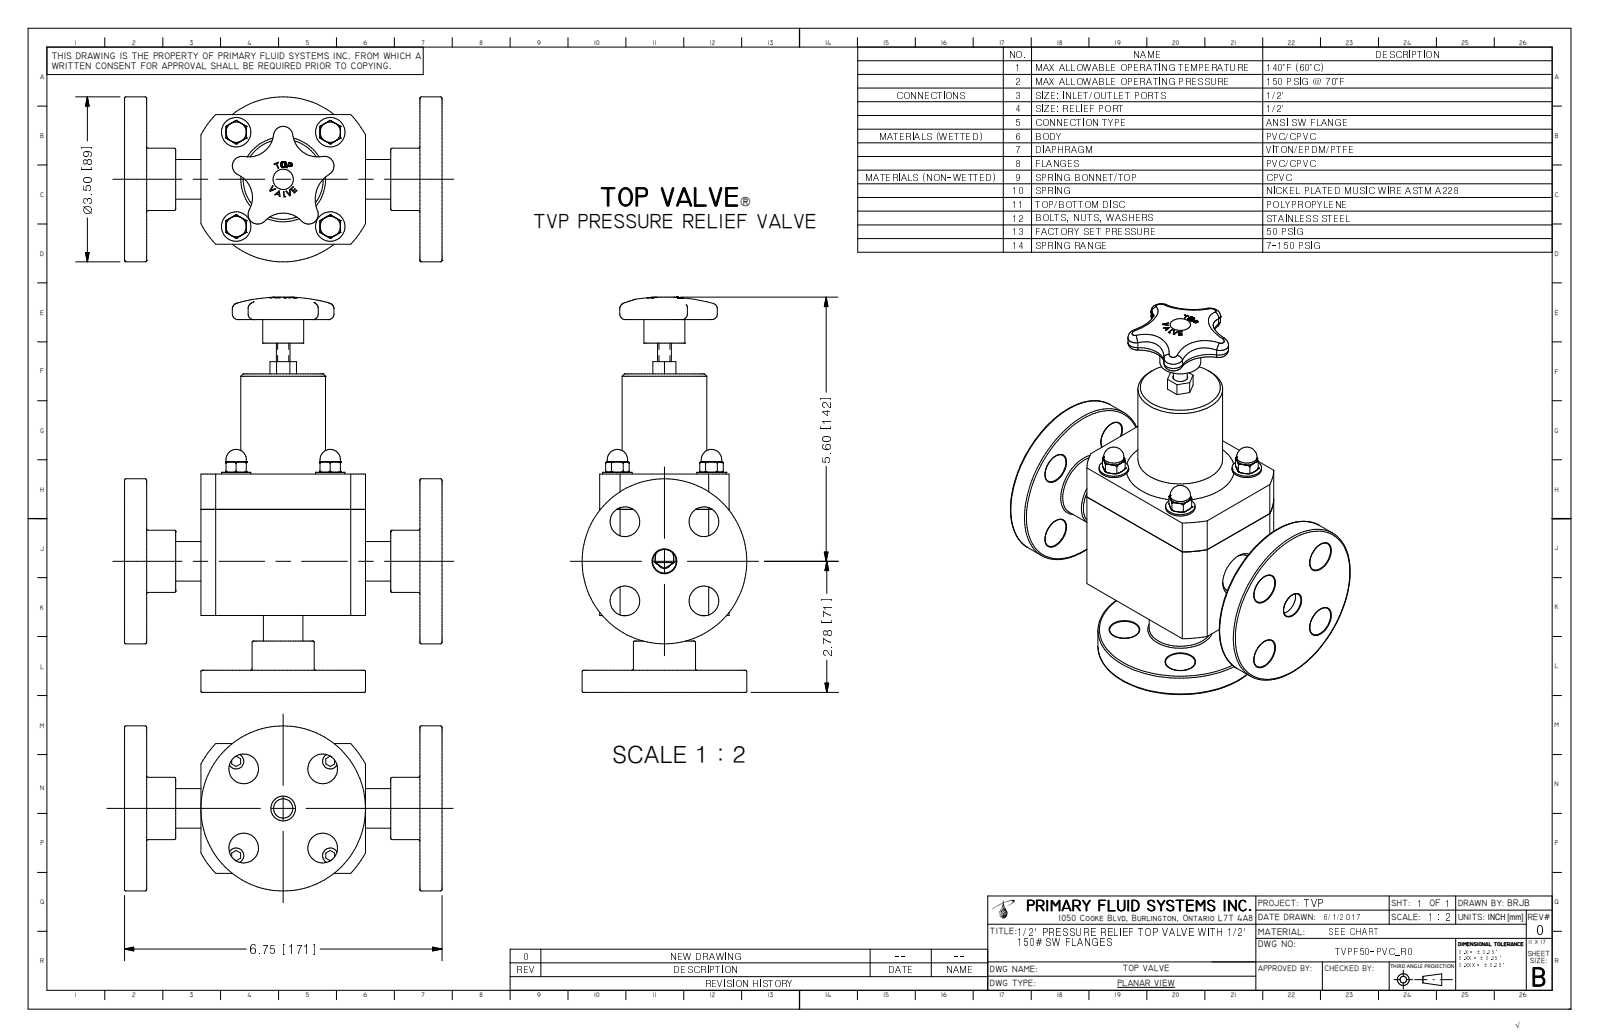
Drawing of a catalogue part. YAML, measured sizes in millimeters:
part_name: "TVPF50-PVC_R0"
step_written_by: "Autodesk Inventor 2009 (AUTOMOTIVE_DESIGN)"
units: millimeters
bodies: {solids: 1, faces: 432, planar: 164, cylindrical: 62, other: 206}
overall_size: [212.9, 171.5, 88.9]
volume: 799700
surface_area: 123000
round_holes:
  - {diameter: 16, count: 8}
  - {diameter: 4.4, count: 4}
  - {diameter: 13.4, count: 2}
  - {diameter: 61, count: 1}
round_bosses_or_shafts:
  - {diameter: 15.9, count: 4}
  - {diameter: 11, count: 4}
  - {diameter: 88.9, count: 2}
  - {diameter: 33.5, count: 2}
  - {diameter: 60.3, count: 1}
  - {diameter: 45.7, count: 1}
  - {diameter: 22.1, count: 1}
  - {diameter: 7.4, count: 1}
partial_cylinders:
  - {radius: 2.2, count: 5}
  - {radius: 5.2, count: 5}
  - {radius: 13.6, count: 4}
  - {radius: 16.7, count: 4}
  - {radius: 15.9, count: 1}
  - {radius: 18.9, count: 1}
  - {radius: 50.5, count: 1}
face_to_face_distances: [11.9, 159.5, 130.2, 41.3, 29.3, 118.2, 69.9, 41.4, 171.5, 29.5]
hole_center_spacings: [30.2, 42.7, 46.9, 5.8, 35.9, 50.8, 60.3, 66.1]
